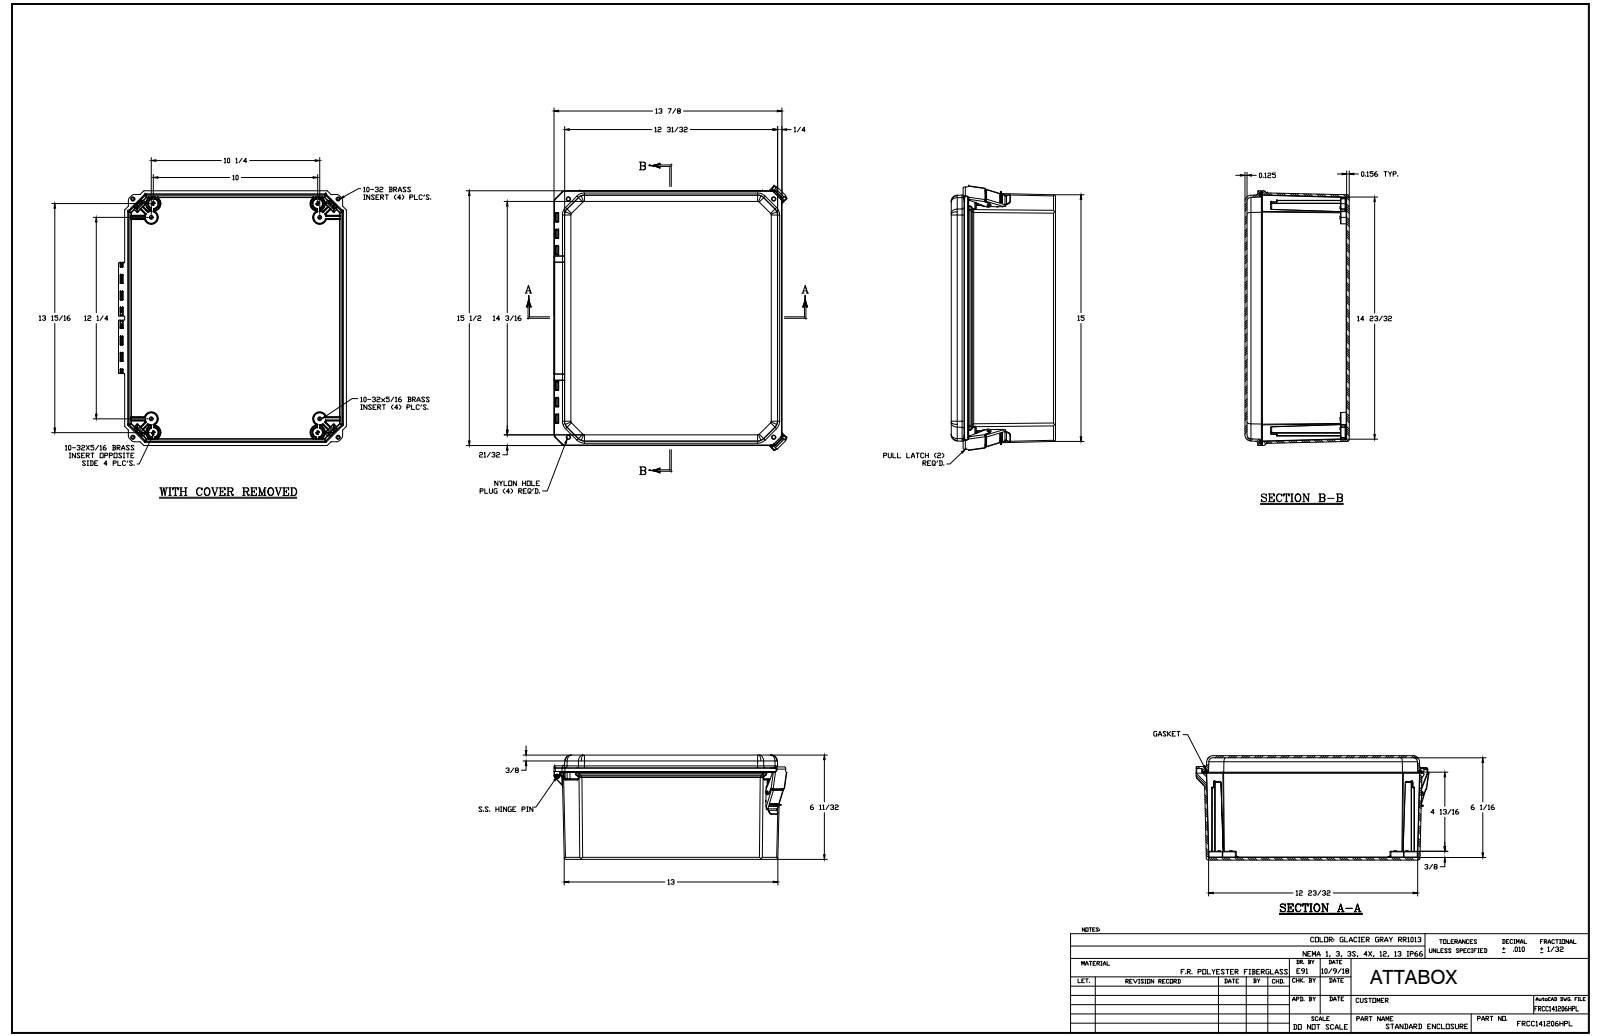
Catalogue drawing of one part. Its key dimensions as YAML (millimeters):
part_name: "FRCC141206HPL"
step_written_by: "SolidWorks 2018 (AUTOMOTIVE_DESIGN)"
units: millimeters
bodies: {solids: 29, faces: 2320, planar: 700, cylindrical: 930, other: 690}
overall_size: [409.7, 360.4, 161.1]
volume: 1817000
surface_area: 1031000
round_holes:
  - {diameter: 4, count: 12}
  - {diameter: 3.4, count: 8}
  - {diameter: 3.9, count: 8}
  - {diameter: 3.8, count: 4}
  - {diameter: 5.6, count: 4}
  - {diameter: 6.4, count: 4}
  - {diameter: 7.9, count: 4}
  - {diameter: 3.4, count: 3}
  - {diameter: 9.5, count: 2}
  - {diameter: 3.5, count: 1}
round_bosses_or_shafts:
  - {diameter: 6.2, count: 12}
  - {diameter: 22.1, count: 4}
  - {diameter: 7.6, count: 4}
  - {diameter: 5.3, count: 4}
  - {diameter: 3.4, count: 3}
partial_cylinders:
  - {radius: 0.3, count: 205}
  - {radius: 0.1, count: 113}
  - {radius: 0.5, count: 59}
  - {radius: 0.8, count: 57}
  - {radius: 3.2, count: 29}
  - {radius: 2.3, count: 26}
  - {radius: 0.8, count: 24}
  - {radius: 1.5, count: 24}
face_to_face_distances: [3.2, 4, 161.1, 157.1, 157.9, 154, 3.6, 3.5, 25.4, 23.8]
hole_center_spacings: [6.4, 368, 340.8, 362.1, 21.4, 32.4, 40.2, 258.1]
